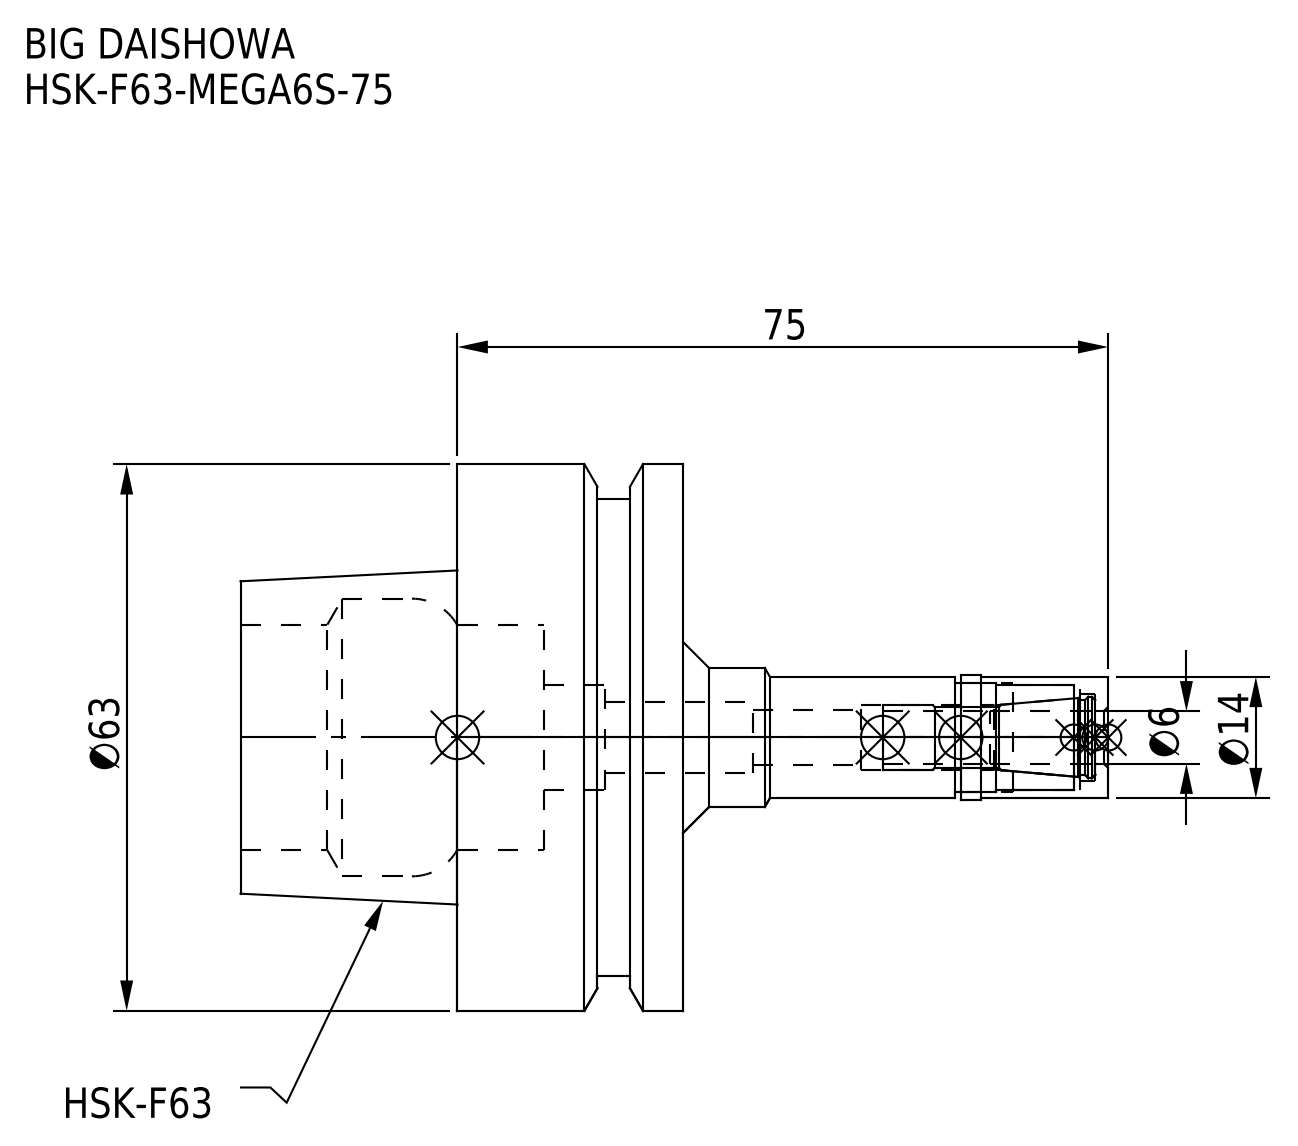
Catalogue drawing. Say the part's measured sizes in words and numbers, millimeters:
The part is named "HSK-F63-MEGA6S-75_1.stp; HSK-F63-MEGA6S-75-060.stp; DXF_TEMP_ASSY_ASM_4_ASM.stp; MGN6S_1.stp (+3 more)". Its 3-D file was written by "SolidWorks 2019 (CONFIG_CONTROL_DESIGN)". It is 2 solids with 78 faces: 18 planar, 42 cylindrical and 18 other. Overall it measures 100 by 63 by 63 millimeters. Its volume is 87 518 cubic millimeters and its surface area 23 405 square millimeters. Round holes: 1 of diameter 6.1, 1 of diameter 6.4, 1 of diameter 7.4, 1 of diameter 8.25, 1 of diameter 10, 1 of diameter 12, 1 of diameter 12.5, 1 of diameter 26, 1 of diameter 32. Round bosses or shafts: 1 of diameter 63, 1 of diameter 55, 1 of diameter 16, 1 of diameter 14.3, 1 of diameter 14. The main face-to-face distances are 26, 51, 25, 16.05, 9.95, 34.95, 6.12, 9.93, 19.88, 44.88.
